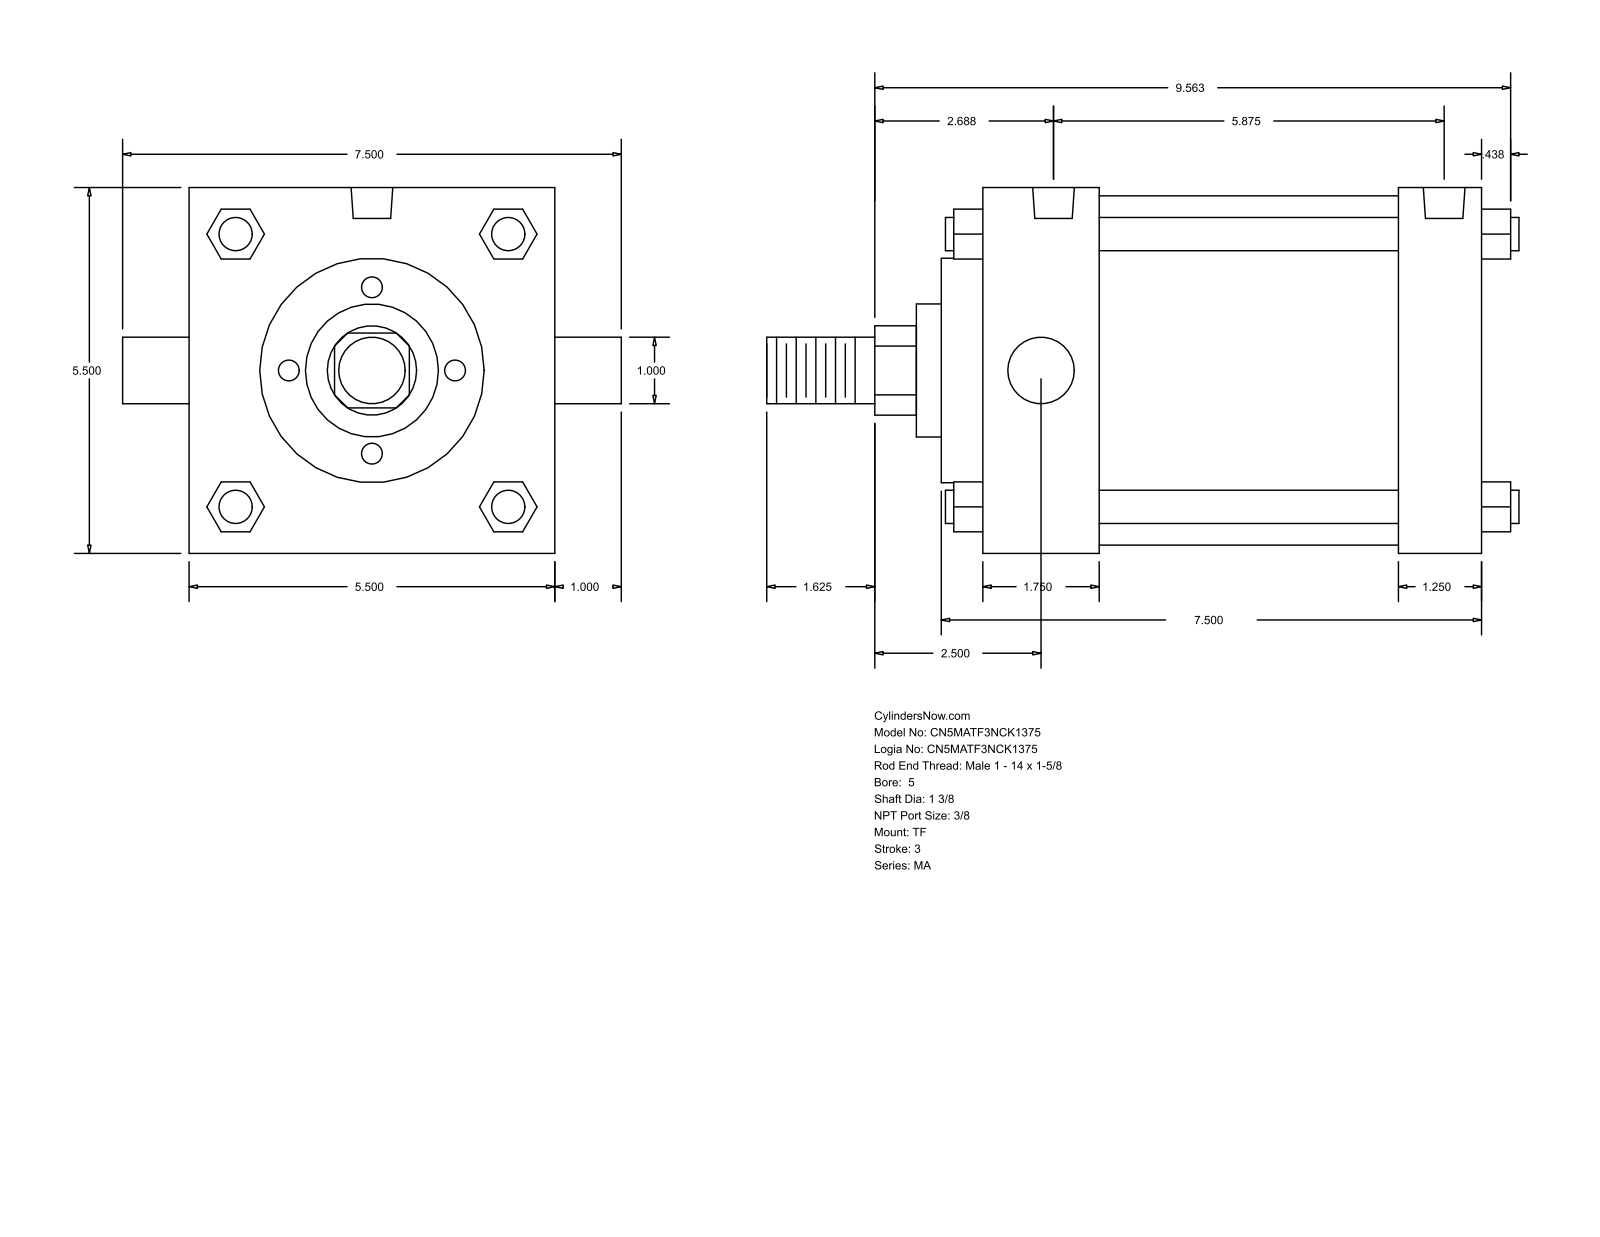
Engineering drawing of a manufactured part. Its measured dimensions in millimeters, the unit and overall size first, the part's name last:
Units: millimetres
Overall size (bounding box): 287.34 × 190.5 × 139.7
Round holes (diameter × count): ⌀11.11 ×3, ⌀15.93 ×2
Round bosses / shafts (diameter × count): ⌀12.7 ×4, ⌀25.4 ×2, ⌀133.35 ×1, ⌀85.72 ×1, ⌀50.8 ×1, ⌀34.92 ×1
Partial cylindrical surfaces — rounded edges, fillets, slot ends (radius × count): R17.06 ×1
Main face-to-face distances: 139.7, 190.51, 158.76, 31.75, 44.45, 114.31, 146.06, 15.87, 60.32, 174.63
Hole centre spacings: 4.77, 144.46, 139.69, 149.23
Bodies: 0 solids, 122 faces (93 planar, 29 cylindrical, 0 other)
Part name (STEP PRODUCT): MA_TF__0500_1.375
STEP written by: GSSL Pune (CONFIG_CONTROL_DESIGN)
